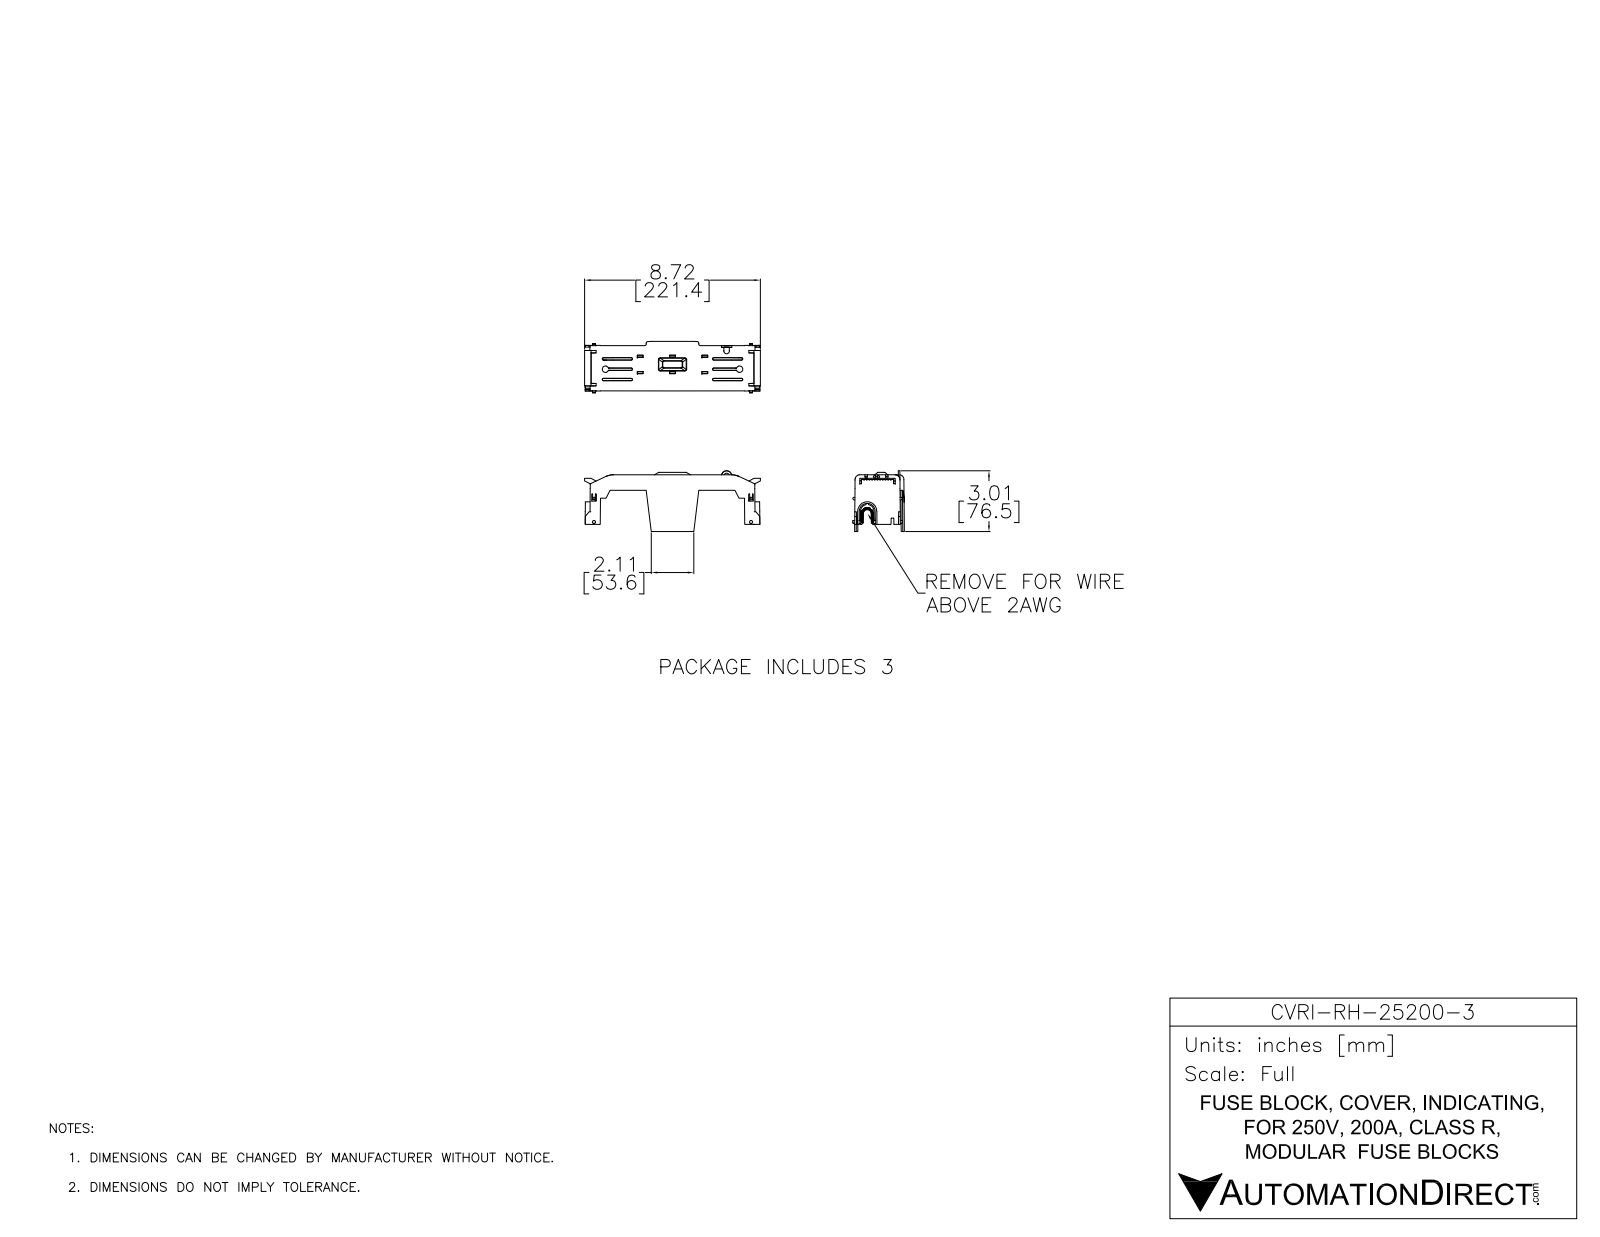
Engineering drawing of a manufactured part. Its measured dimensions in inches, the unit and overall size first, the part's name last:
Units: inches
Overall size (bounding box): 8.715 × 3.012 × 2.554
Round holes (diameter × count): ⌀0.276 ×1
Partial cylindrical surfaces — rounded edges, fillets, slot ends (radius × count): R0.039 ×16, R0.236 ×9, R0.118 ×8, R0.157 ×7, R0.079 ×6, R0.01 ×2, R0.02 ×2, R0.63 ×2
Main face-to-face distances: 0.079, 0.197, 0.118, 0.276, 0.803, 0.604, 1.661, 1.74, 1.286, 1.365
Volume: 4.617 in³ · Surface area: 125 in²
Bodies: 1 solid, 1406 faces (950 planar, 105 cylindrical, 351 other)
Part name (STEP PRODUCT): CVRI-RH-25200-3
STEP written by: SolidWorks 2017 (AUTOMOTIVE_DESIGN)
